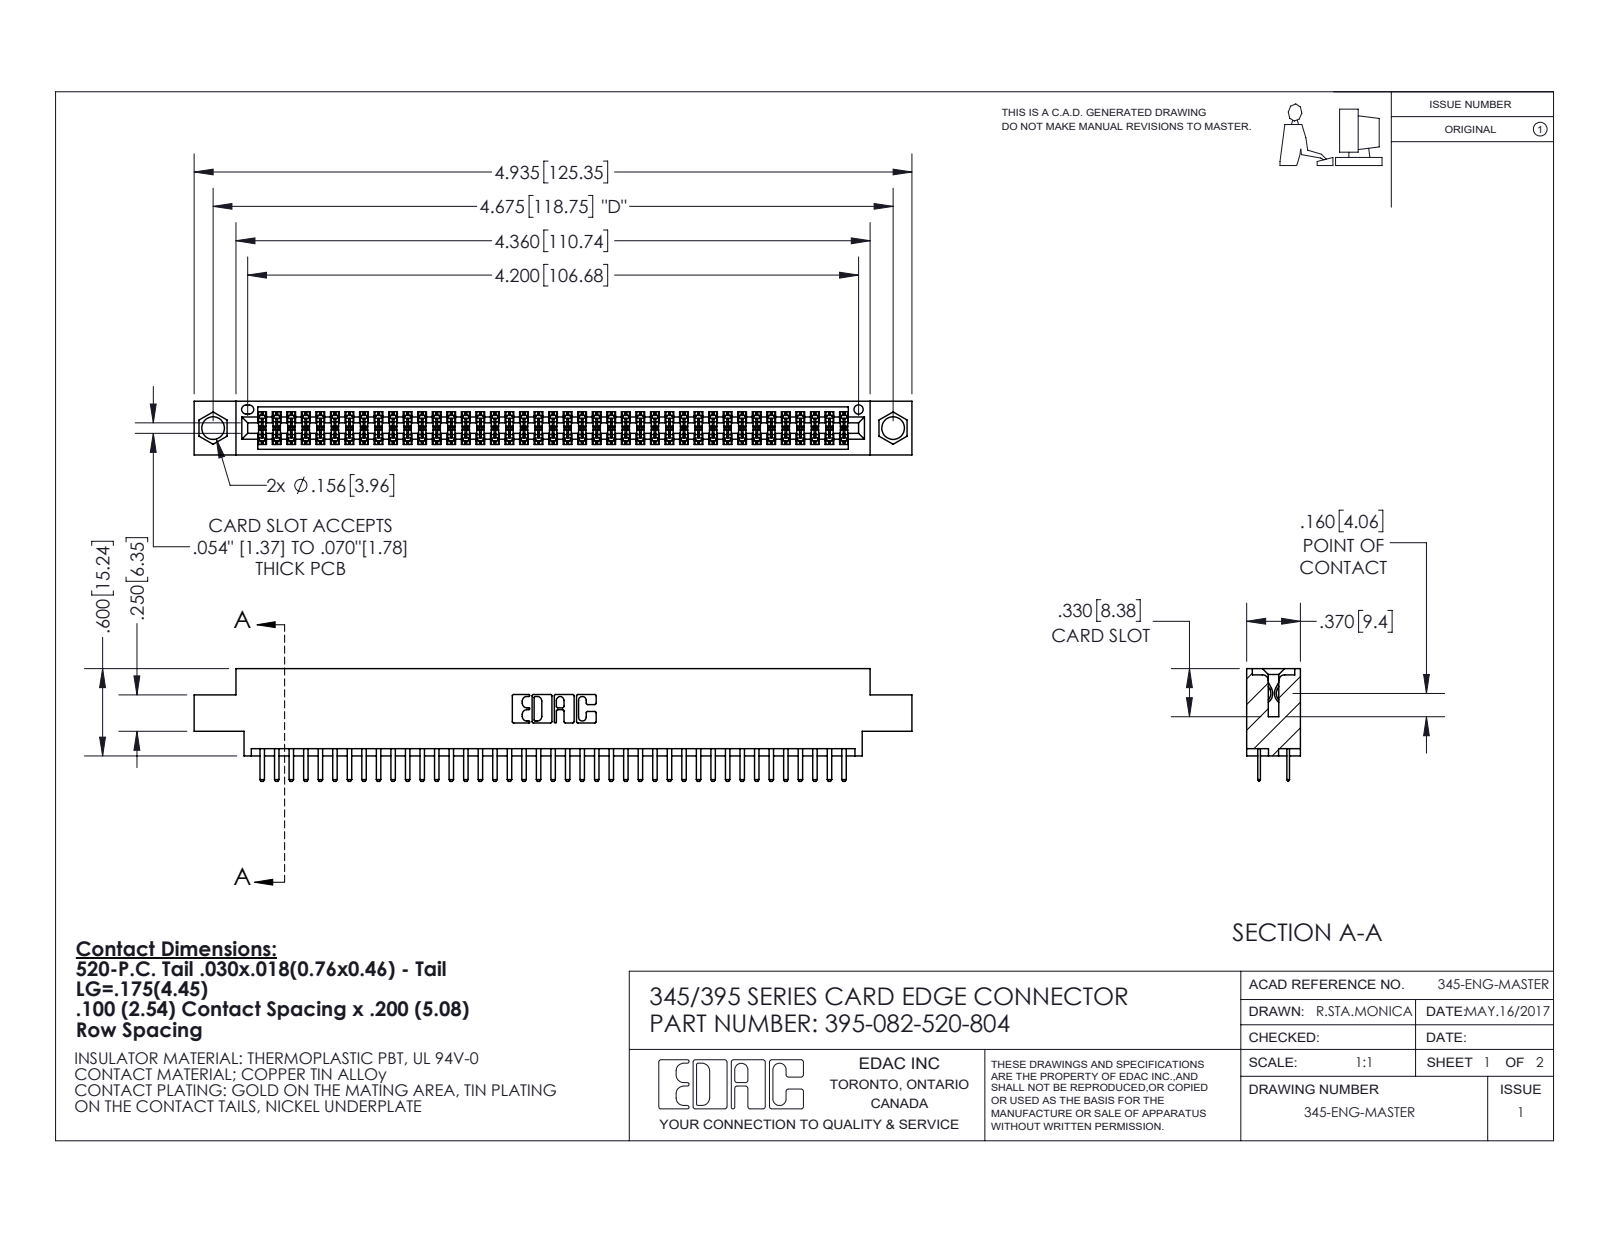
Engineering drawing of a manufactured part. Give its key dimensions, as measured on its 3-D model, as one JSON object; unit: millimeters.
{"part_name": "395-082-520-804; 345 Part_0.170 Offset - 0.156 Dia-TI; 345-292-001_345-293-120", "step_written_by": "SolidWorks 2020 (CONFIG_CONTROL_DESIGN)", "units": "millimeters", "bodies": {"solids": 83, "faces": 4572, "planar": 2968, "cylindrical": 1604, "other": 0}, "overall_size": [125.3, 19.7, 9.4], "volume_mm3": 11900, "surface_area_mm2": 17510, "round_holes": [[4, 2], [1.6, 1]], "partial_cylinders_radius": [[0.2, 164], [0.3, 86], [0.3, 22], [0.2, 6], [0.8, 6], [0.7, 3], [0.4, 2], [0.5, 2]], "face_to_face_distances": [1.8, 7.6, 5.1, 9.4, 2.5, 6.9, 0.6, 5.7, 0.6, 4.4], "hole_center_spacings": [6.9, 112.8, 118.7]}
